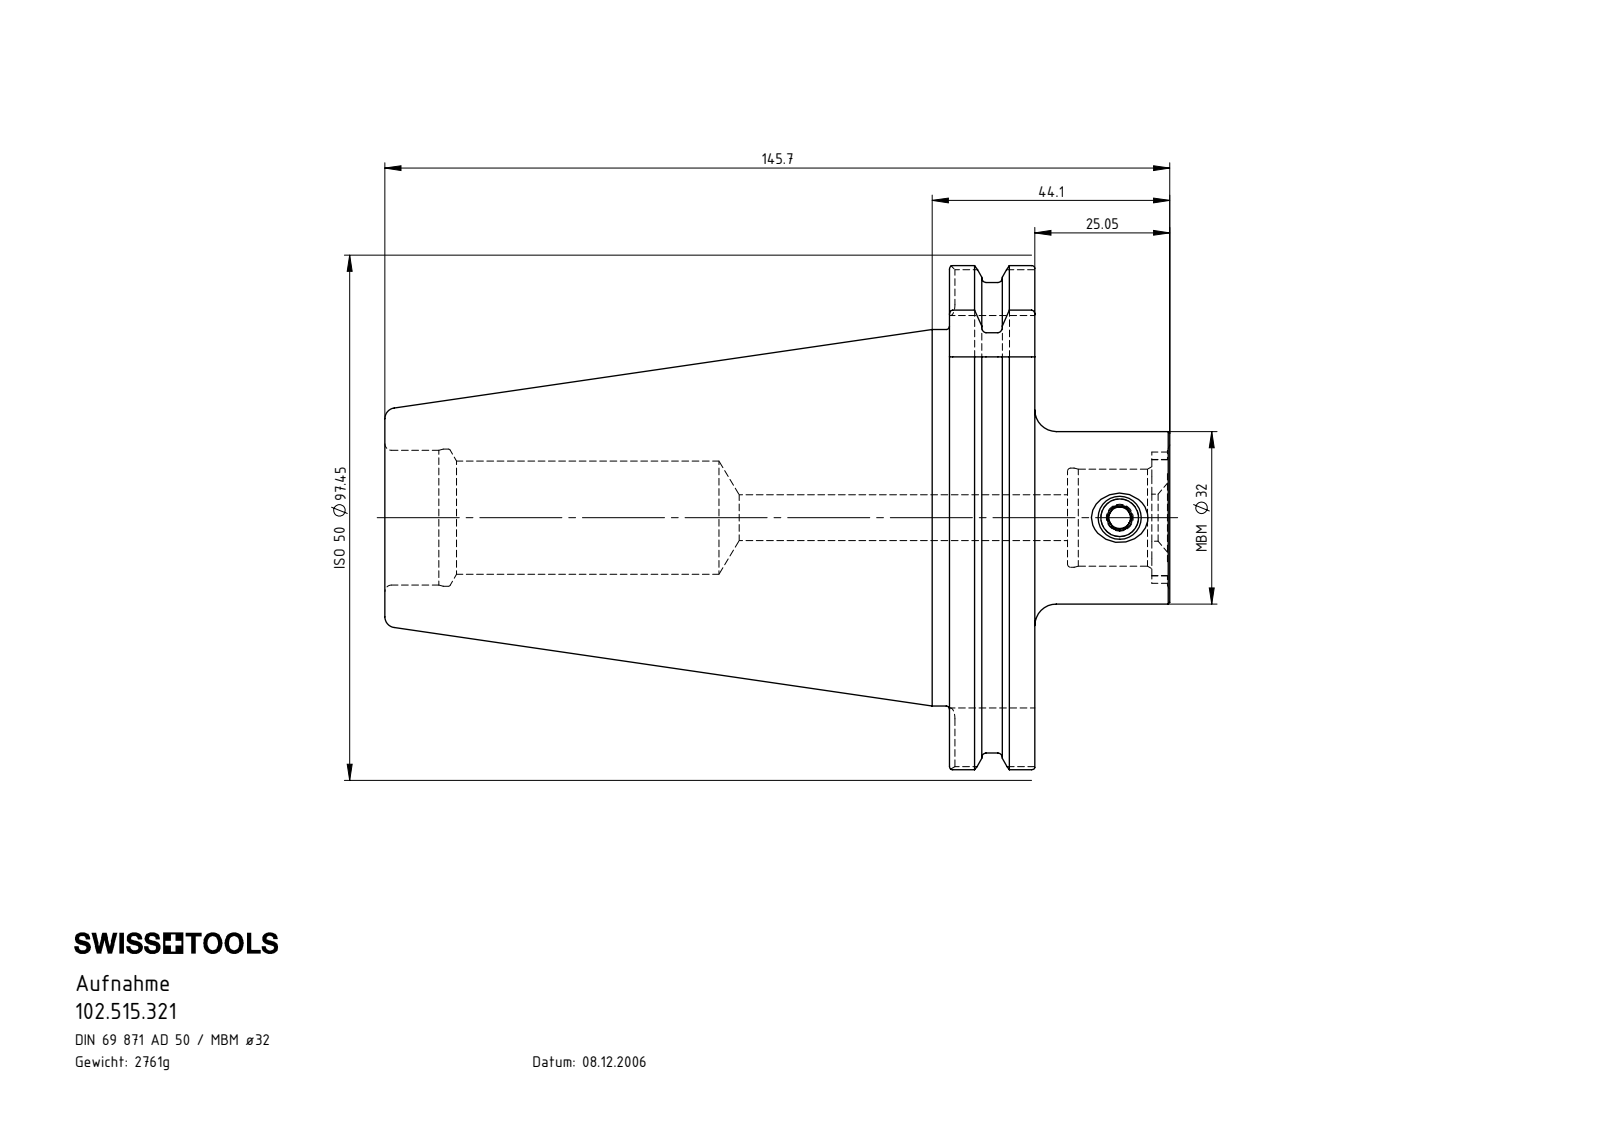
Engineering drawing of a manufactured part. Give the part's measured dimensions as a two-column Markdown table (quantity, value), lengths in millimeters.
| quantity | value |
| --- | --- |
| part name | 102.515.321; SK5-MB3.K01.044_C; MB3-ER1.001.011_A |
| STEP written by | SolidWorks 2017 (CONFIG_CONTROL_DESIGN) |
| units | millimeters |
| bodies | 2 solids, 171 faces (55 planar, 50 cylindrical, 66 other) |
| overall size | 145.7 × 97.45 × 93.51 |
| volume | 351 677 mm³ |
| surface area | 45 059 mm² |
| round holes (diameter × count) | 4 × 1, 7 × 1, 8.5 × 1, 18 × 1, 18.4 × 1, 21 × 1, 25 × 1, 25.45 × 1 |
| round bosses / shafts (diameter × count) | 91 × 1, 69.85 × 1, 32 × 1, 8 × 1 |
| partial cylindrical surfaces (radius × count) | 2 × 8, 3.2 × 4, 12.18 × 1, 48.73 × 1 |
| main face-to-face distances | 15.85, 104.8, 120.65, 72.8, 25.7, 145.7, 40.9, 25.05, 126.7, 21.9 |
